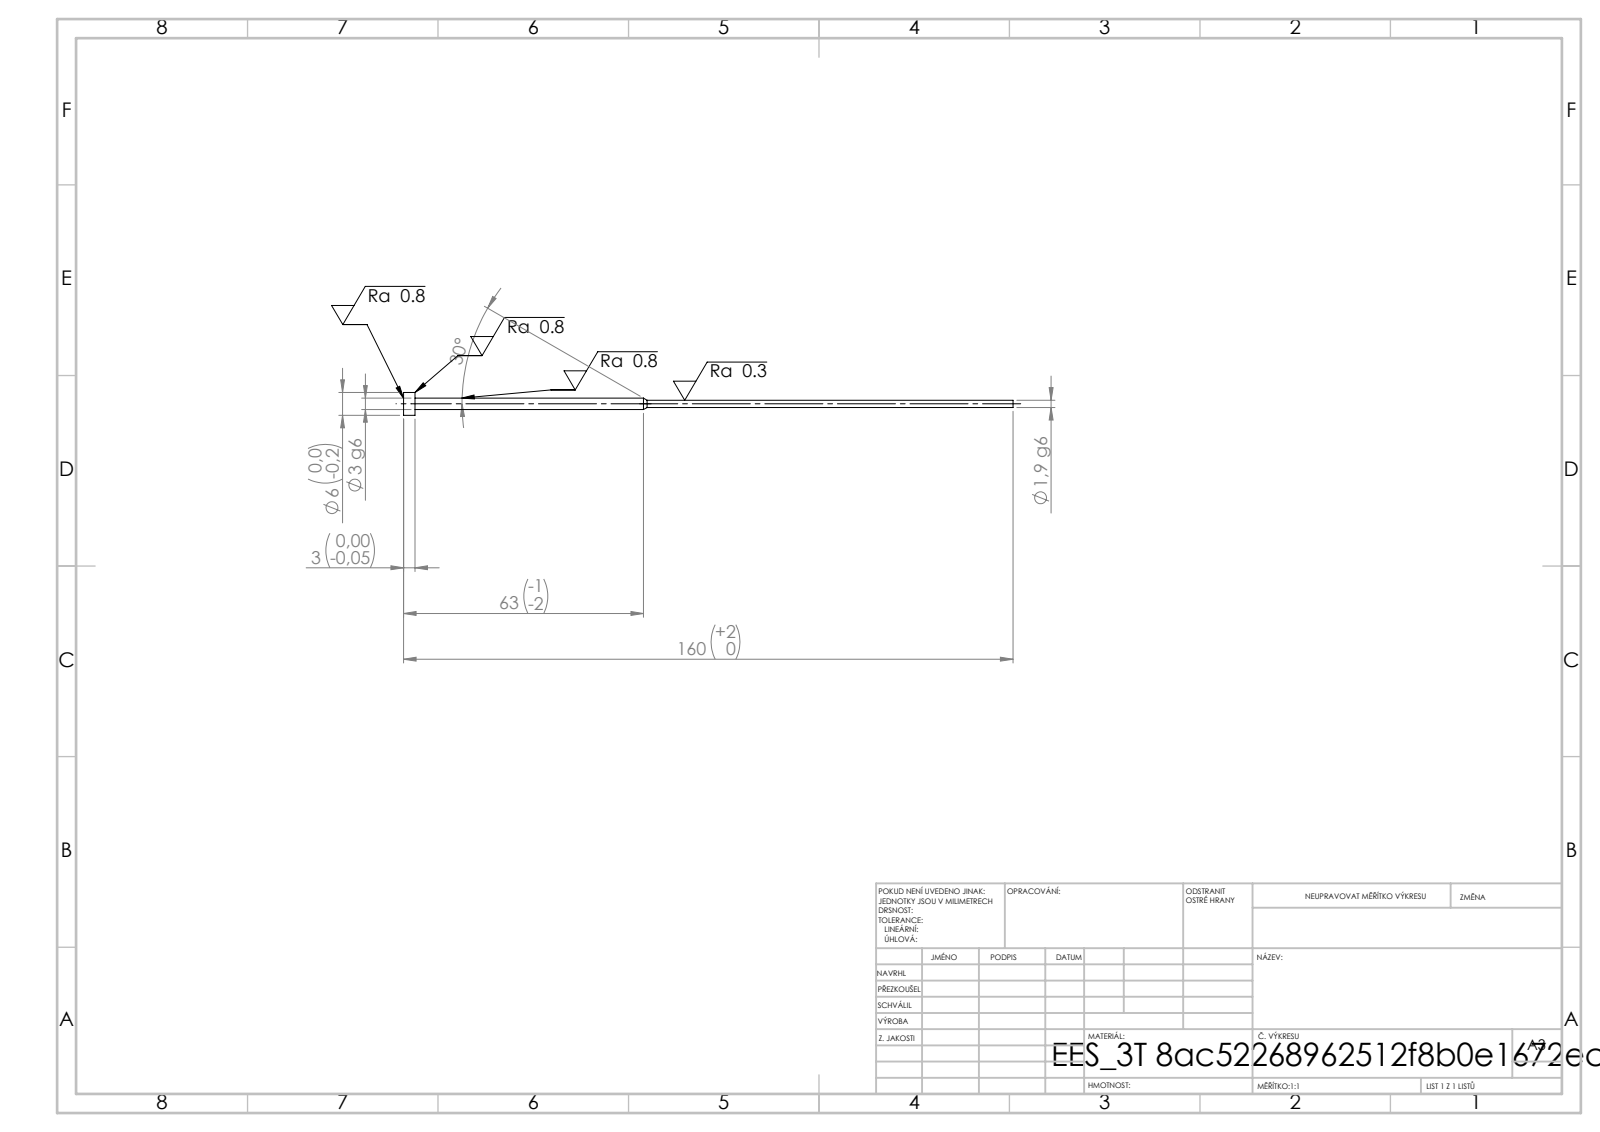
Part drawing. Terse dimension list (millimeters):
written by: SolidWorks 2019 (CONFIG_CONTROL_DESIGN)
unit: mm
bodies: 1 solid, 11 faces (3 planar, 6 cylindrical, 2 other)
size: 160 × 6 × 6
volume: 786 mm³; area: 1 256 mm²
bosses: 1× ⌀6, 1× ⌀3, 1× ⌀1.9
face distances: 3, 157, 160
